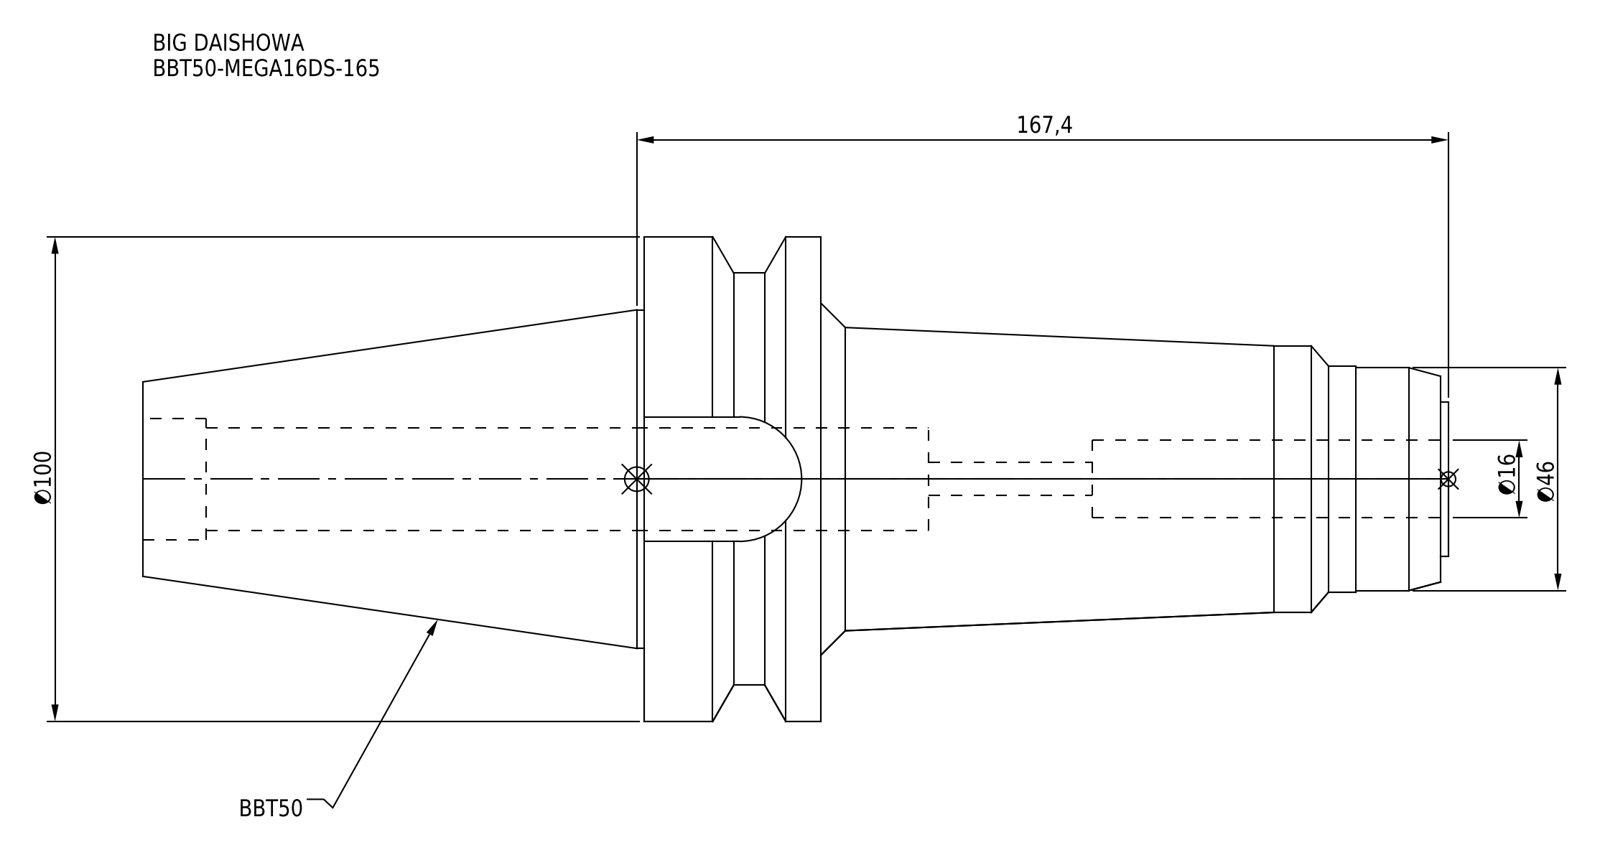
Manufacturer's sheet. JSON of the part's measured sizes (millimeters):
{"part_name": "BBT50-MEGA16DS-165", "step_written_by": "CREO PARAMETRIC BY PTC INC, 2016380 (AUTOMOTIVE_DESIGN)", "units": "millimeters", "bodies": {"solids": 1, "faces": 57, "planar": 15, "cylindrical": 28, "other": 14}, "overall_size": [269.2, 100, 100], "volume_mm3": 746988, "surface_area_mm2": 81528, "round_holes": [[6.8, 1], [16, 1], [21.2, 1], [25, 1]], "round_bosses_or_shafts": [[100, 1], [85, 1], [69.85, 1], [55, 1], [46.7, 1], [46, 1], [31.9, 1]], "partial_cylinders_radius": [[12.85, 1]], "face_to_face_distances": [36.5, 139.8, 103.3, 70.8, 127.8, 164.3, 267.6, 1.6, 129.4, 165.9]}
